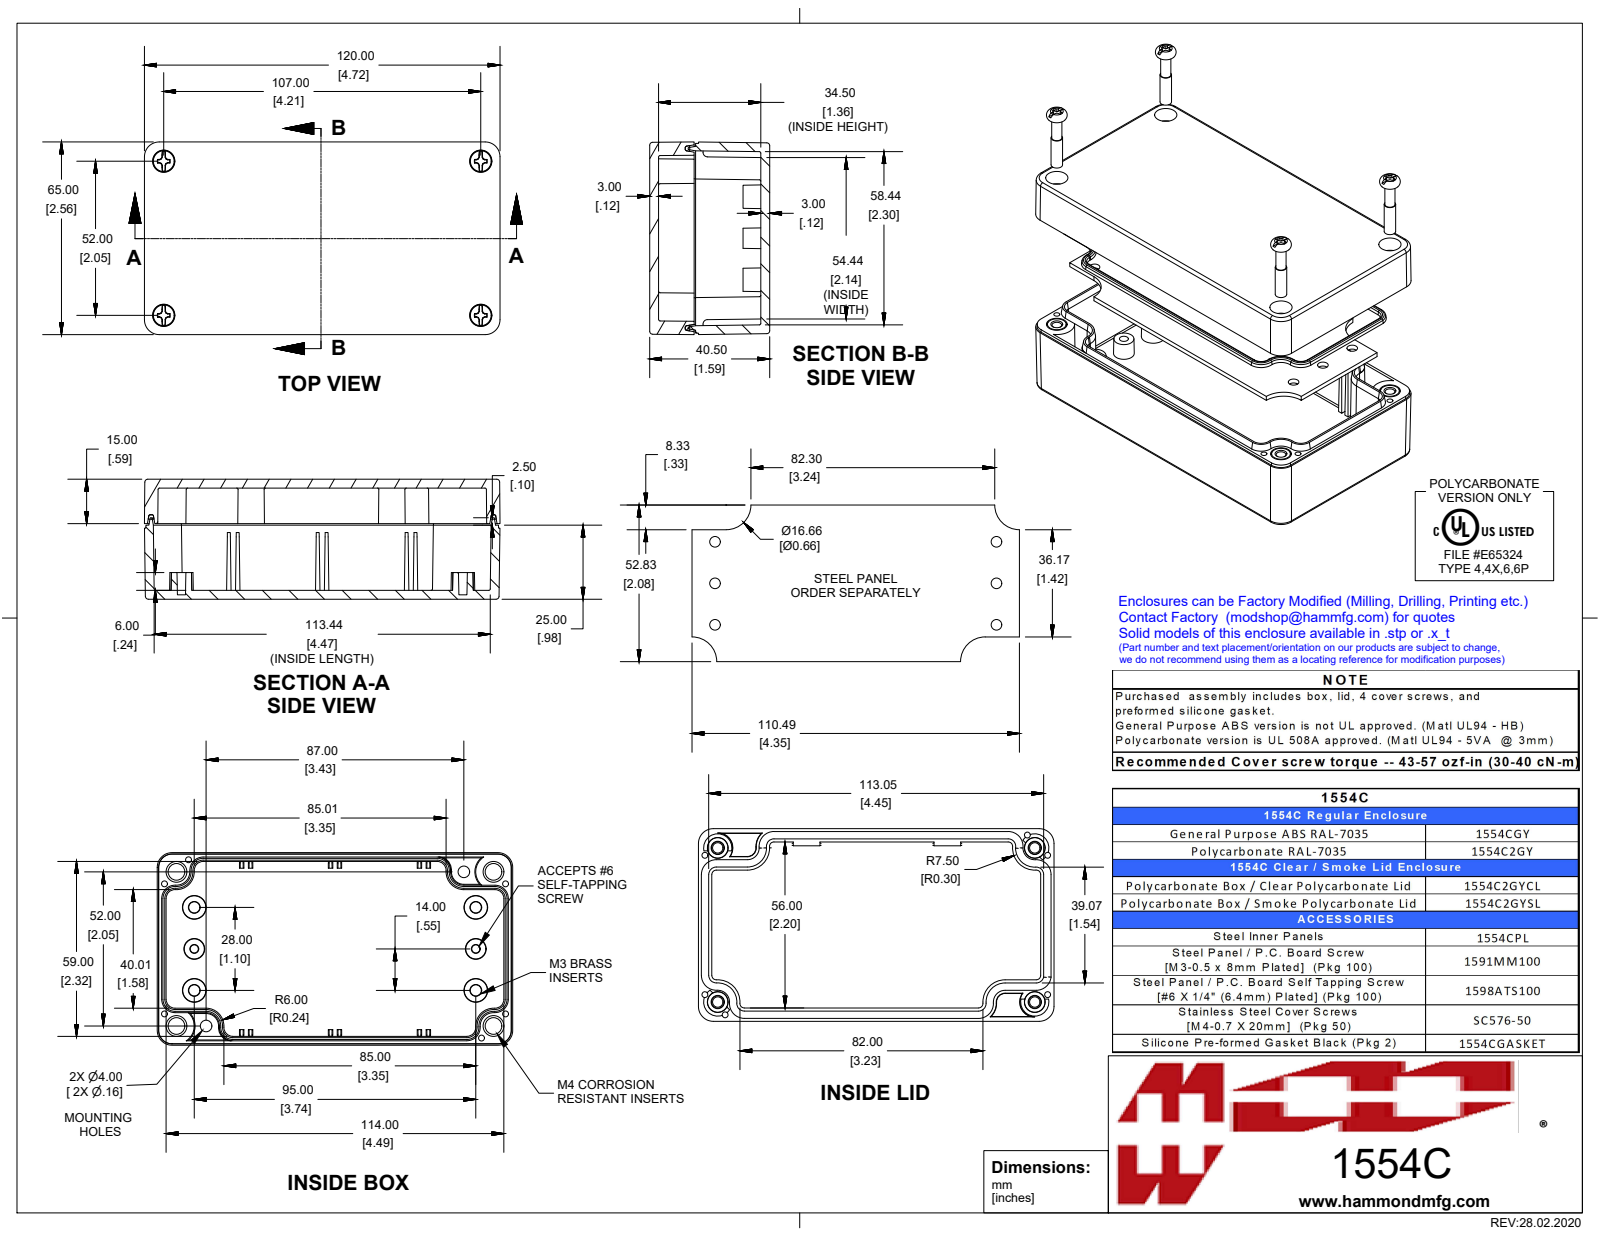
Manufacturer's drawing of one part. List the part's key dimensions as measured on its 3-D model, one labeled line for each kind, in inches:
Part name (STEP PRODUCT): 1554CGY
STEP written by: SolidWorks 2019 (AUTOMOTIVE_DESIGN)
Units: inches
Bodies: 15 solids, 1294 faces (342 planar, 338 cylindrical, 614 other)
Overall size (bounding box): 4.724 × 2.559 × 1.594
Volume: 5.948 in³ · Surface area: 112.5 in²
Round holes (diameter × count): ⌀0.079 ×12, ⌀0.097 ×4, ⌀0.128 ×4, ⌀0.138 ×4, ⌀0.276 ×4
Round bosses / shafts (diameter × count): ⌀0.25 ×4, ⌀0.218 ×4, ⌀0.21 ×4, ⌀0.19 ×4, ⌀0.154 ×4, ⌀0.153 ×4, ⌀0.15 ×4, ⌀0.135 ×4
Partial cylindrical surfaces — rounded edges, fillets, slot ends (radius × count): R0.02 ×36, R0.039 ×8, R0.197 ×8, R0.187 ×4, R0.059 ×2
Main face-to-face distances: 0.118, 1.476, 1.594, 1.358, 0.059, 0.177, 0.492, 0.079, 1.004, 0.472
Hole centre spacings: 0.197, 0.226, 0.42, 1.956, 4.384, 4.684, 4.797, 0.062
